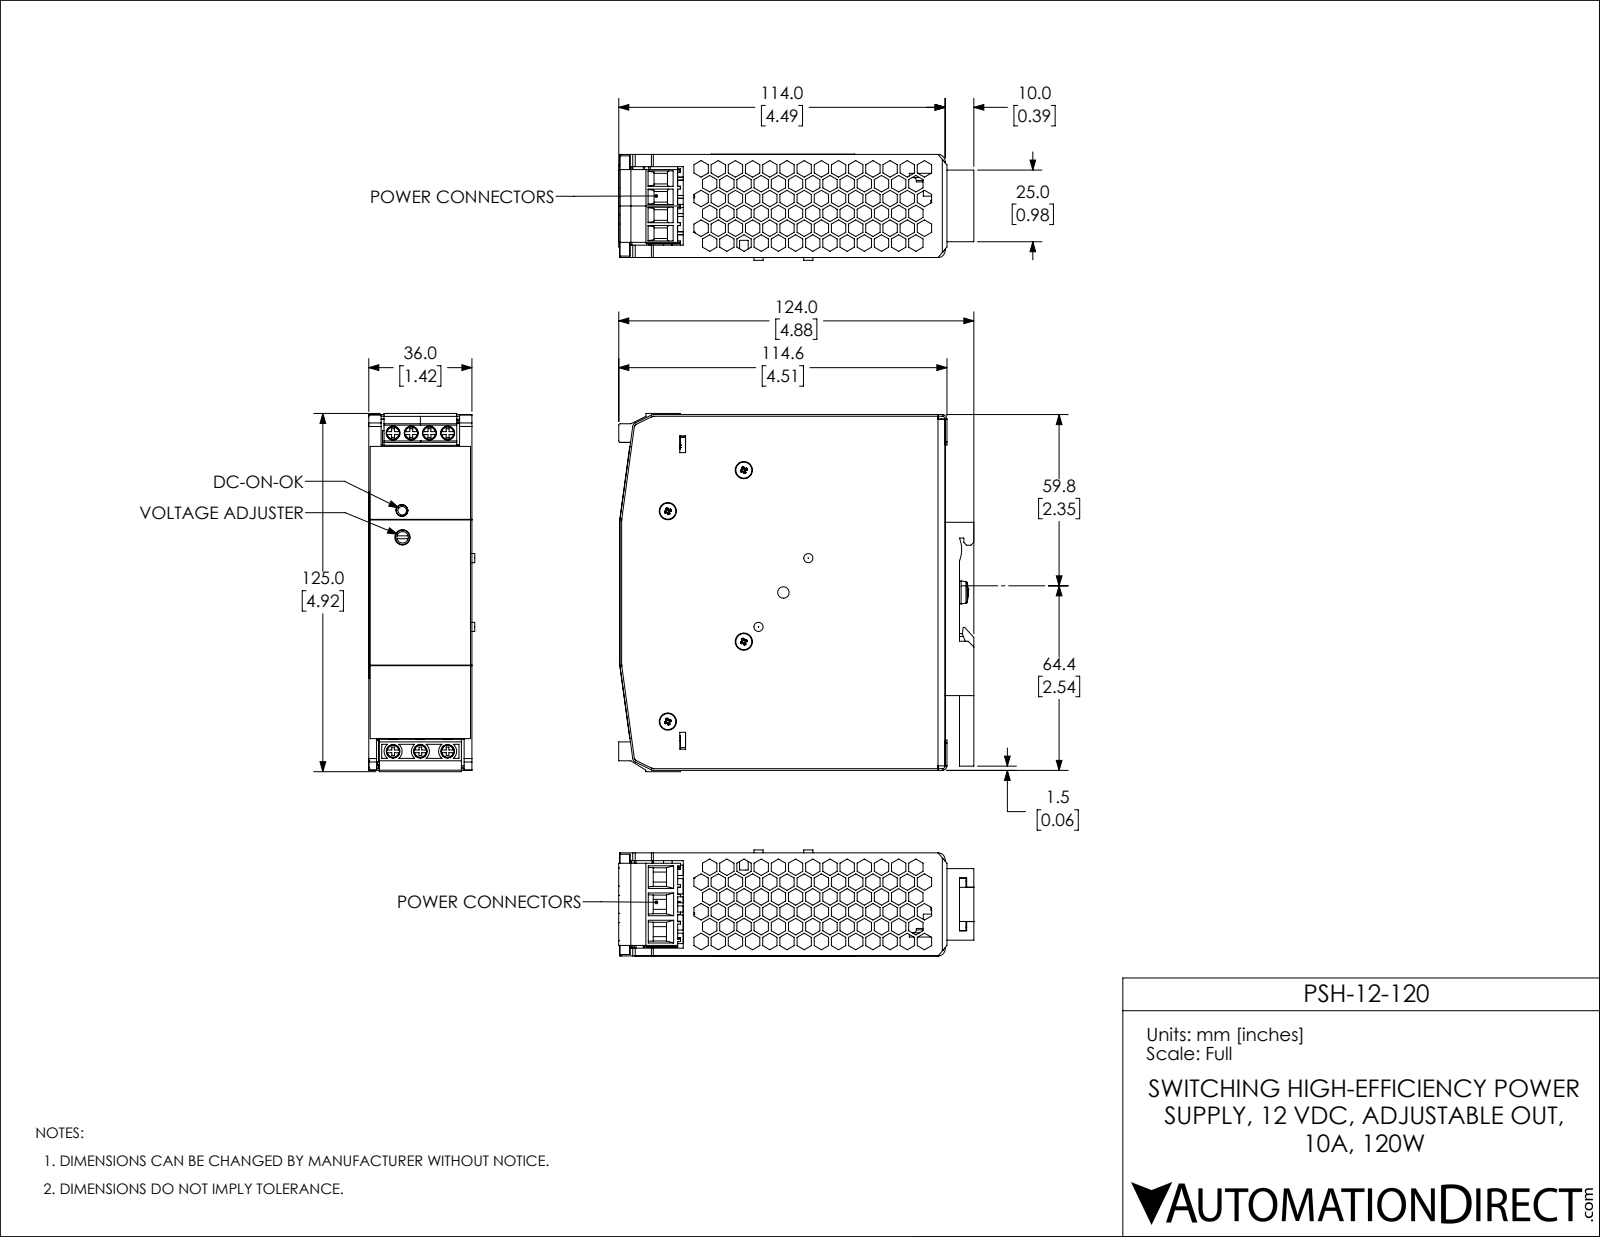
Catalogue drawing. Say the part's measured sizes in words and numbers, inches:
The part is named "PSH-X-120". Its 3-D file was written by "SolidWorks 2017 (AUTOMOTIVE_DESIGN)". It is 16 solids with 2175 faces: 1825 planar, 206 cylindrical and 144 other. Overall it measures 4.923 by 4.884 by 1.459 inches. Its volume is 4.497 cubic inches and its surface area 178.1 square inches. Round holes: 6 of diameter 0.008, 4 of diameter 0.118, 4 of diameter 0.138, 4 of diameter 0.157, 4 of diameter 0.181, 4 of diameter 0.193, 4 of diameter 0.193, 3 of diameter 0.177, 3 of diameter 0.189, 2 of diameter 0.097, 2 of diameter 0.126, 2 of diameter 0.146. Round bosses or shafts: 6 of diameter 0.126, 6 of diameter 0.118, 5 of diameter 0.22, 5 of diameter 0.157, 5 of diameter 0.02, 4 of diameter 0.187, 3 of diameter 0.188, 1 of diameter 0.079. Partial cylindrical surfaces (rounded edges, fillets, slot ends): 22 of radius 0.039, 16 of radius 0.004, 9 of radius 0.063, 7 of radius 0.006, 6 of radius 0.098, 4 of radius 0.02, 4 of radius 0.092, 3 of radius 0.124. The main face-to-face distances are 0.059, 1.358, 1.417, 1.299, 0.024, 4.413, 4.472, 0.061, 1.36, 1.419. The hole center spacings are 0.25, 0.376, 0.583, 0.152, 0.315, 0.323, 0.326, 0.334.
